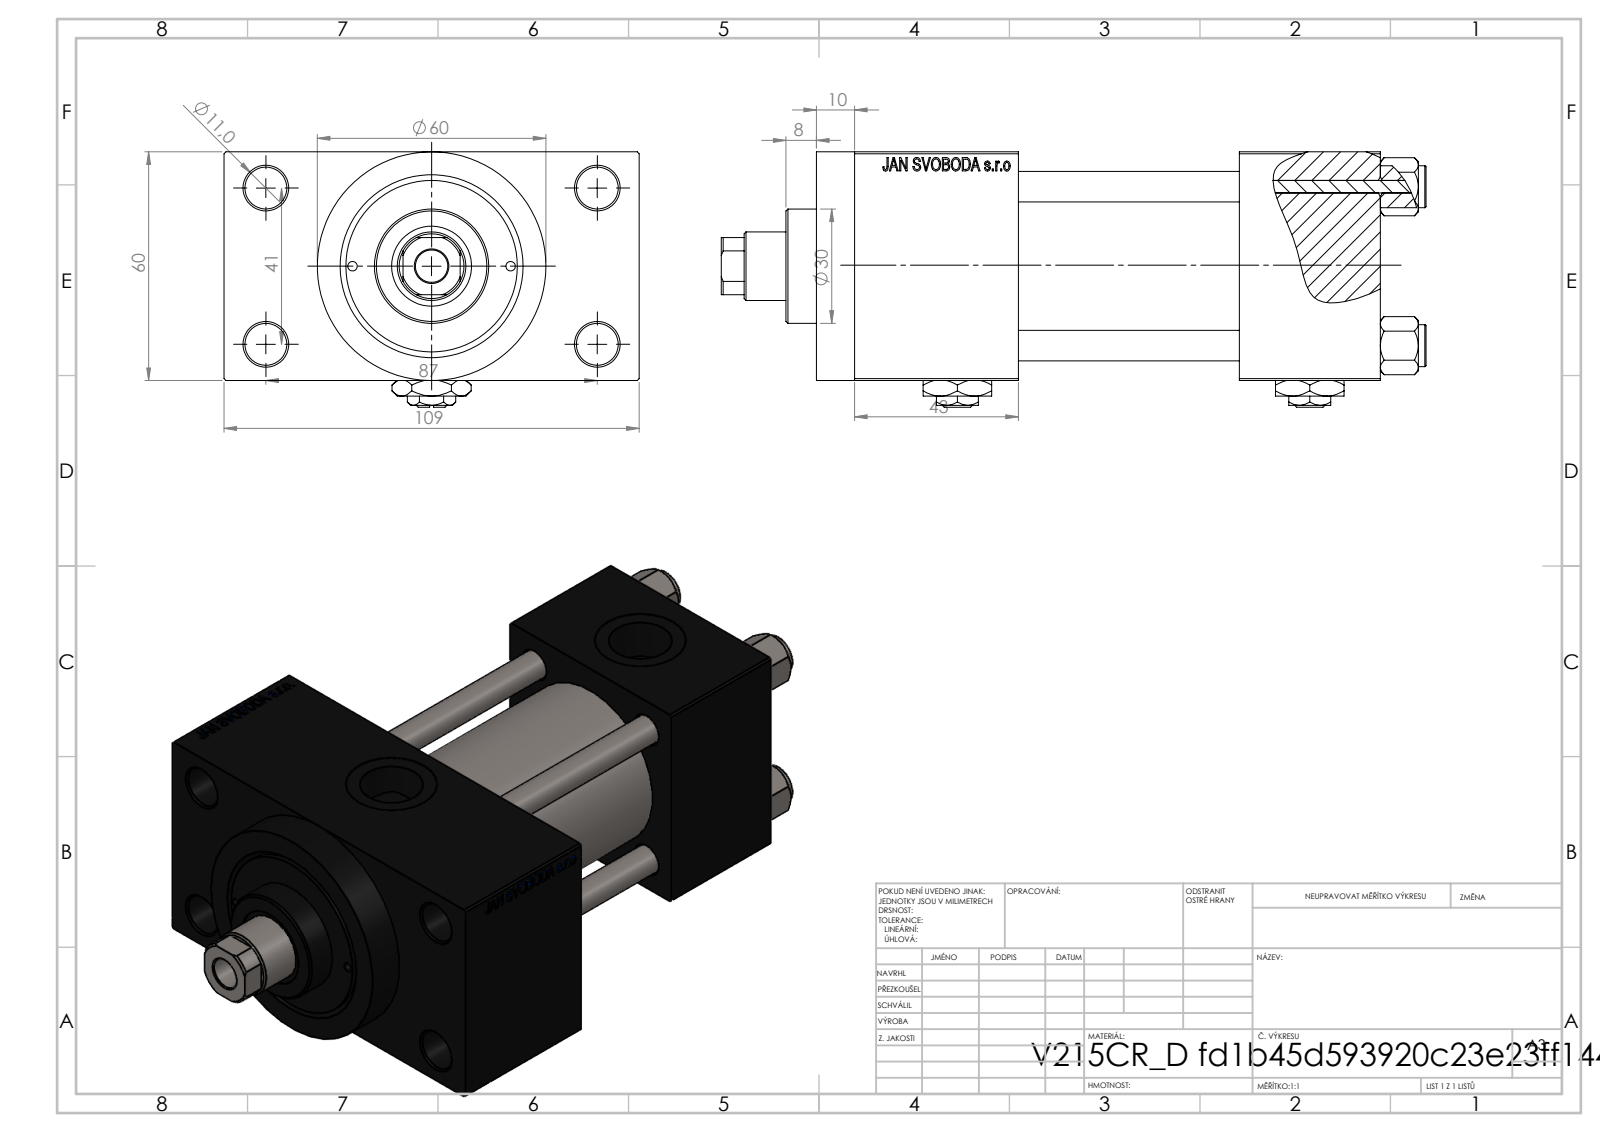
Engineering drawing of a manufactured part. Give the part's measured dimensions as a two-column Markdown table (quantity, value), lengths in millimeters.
| quantity | value |
| --- | --- |
| part name | NUT_M5_D; V215_VC_A; V215CR_D_TYCINKA; Zatka_pro_OIL_PORT (+2 more) |
| STEP written by | SolidWorks 2019 (CONFIG_CONTROL_DESIGN) |
| units | millimeters |
| bodies | 13 solids, 1214 faces (548 planar, 104 cylindrical, 562 other) |
| overall size | 185 × 109 × 67 |
| volume | 515 380 mm³ |
| surface area | 123 872 mm² |
| round holes (diameter × count) | 8 × 4, 11 × 4, 2.5 × 2, 7 × 2, 16.66 × 2, 24 × 2, 8.5 × 1, 18 × 1, 21 × 1, 31 × 1, 40 × 1, 45 × 1 |
| round bosses / shafts (diameter × count) | 11 × 4, 60 × 1, 46 × 1, 30 × 1 |
| partial cylindrical surfaces (radius × count) | 8.5 × 1 |
| main face-to-face distances | 60, 24.5, 84.5, 58, 37, 95, 43, 138, 101, 109 |
| hole center spacings | 20.85, 22.65, 29.49, 30.62, 41.7, 46.53, 47.15, 48.09 |
